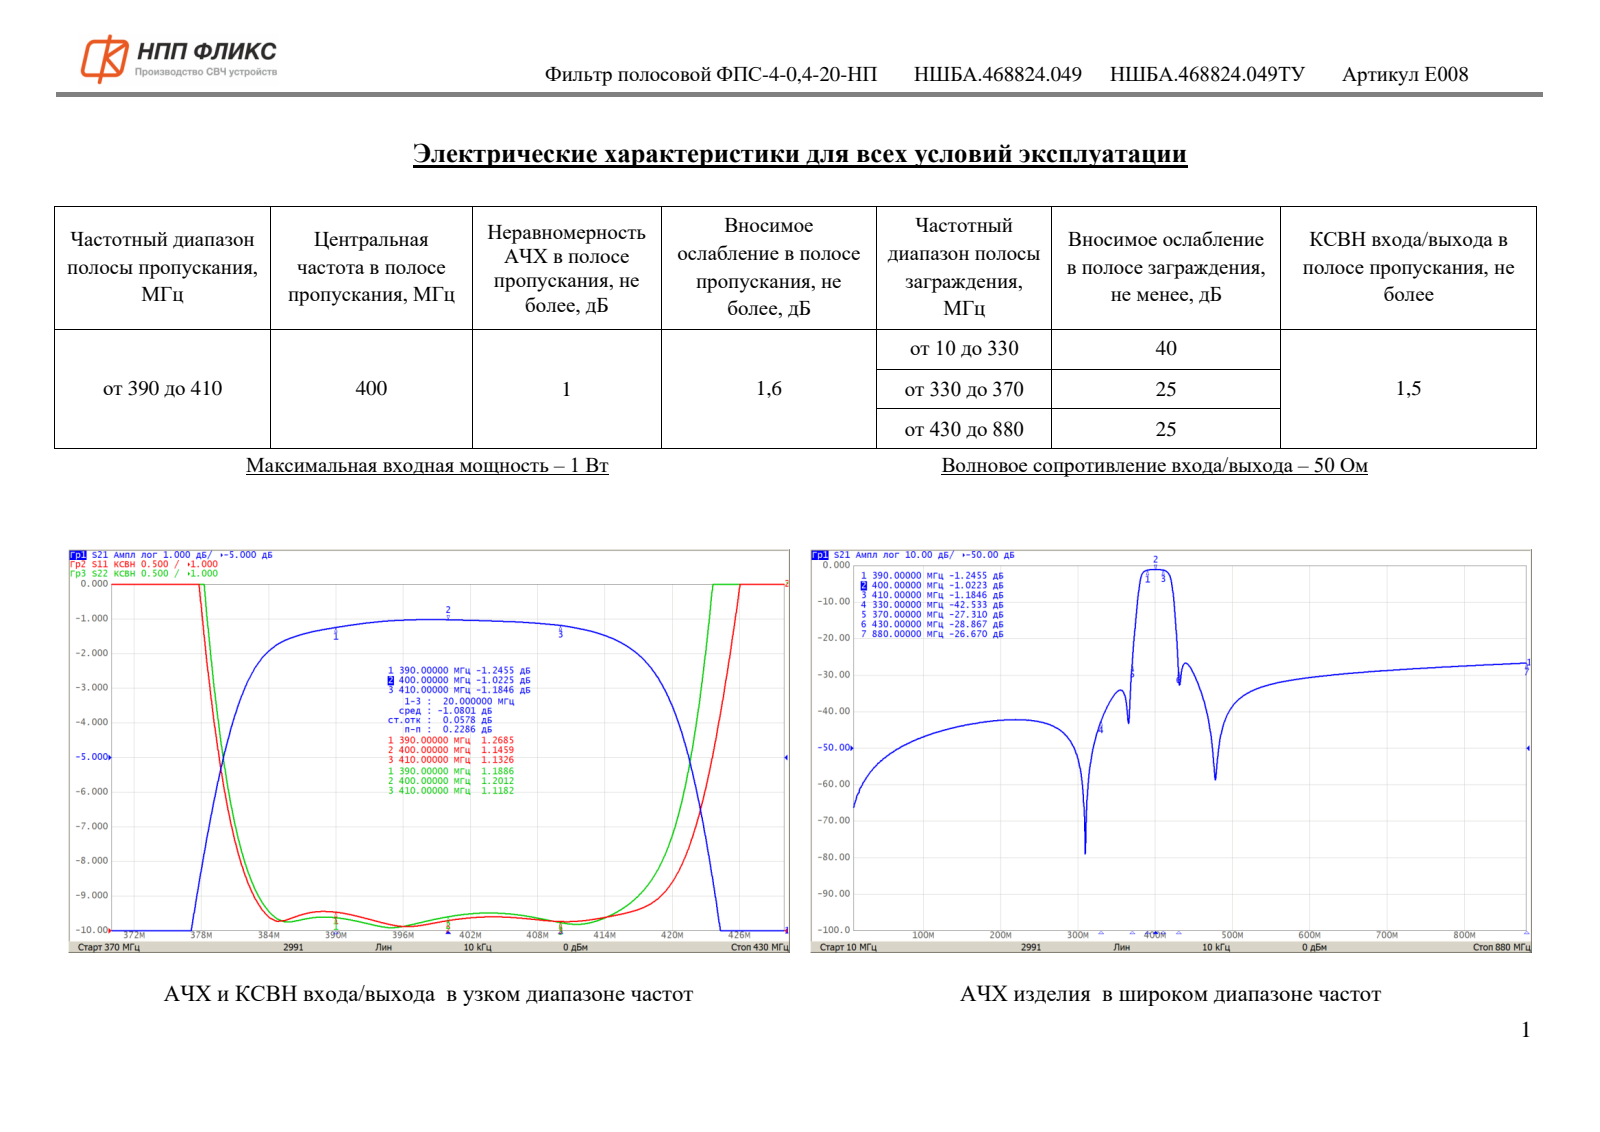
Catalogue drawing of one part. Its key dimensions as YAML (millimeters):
part_name: "НШБА.468824.049_Фильтр ФПС-4-0,4-20-НП"
step_written_by: "ASCON Math Kernel (CONFIG_CONTROL_DESIGN)"
units: millimeters
bodies: {solids: 1, faces: 685, planar: 491, cylindrical: 81, other: 113}
overall_size: [25, 17, 8.91]
volume: 638
surface_area: 2859
round_holes:
  - {diameter: 0.7, count: 6}
  - {diameter: 0.5, count: 2}
partial_cylinders:
  - {radius: 0.4, count: 18}
  - {radius: 0.3, count: 8}
  - {radius: 0.45, count: 8}
  - {radius: 0.6, count: 8}
  - {radius: 1, count: 8}
  - {radius: 0.5, count: 3}
  - {radius: 0.25, count: 1}
  - {radius: 0.75, count: 1}
face_to_face_distances: [0.81, 15.3, 8.1, 8.91, 8.61, 7.8, 23.3, 15, 15.6, 23.6]
hole_center_spacings: [5.66, 10.04, 12.54, 13.6, 18.19, 10, 15.3, 18.28]
